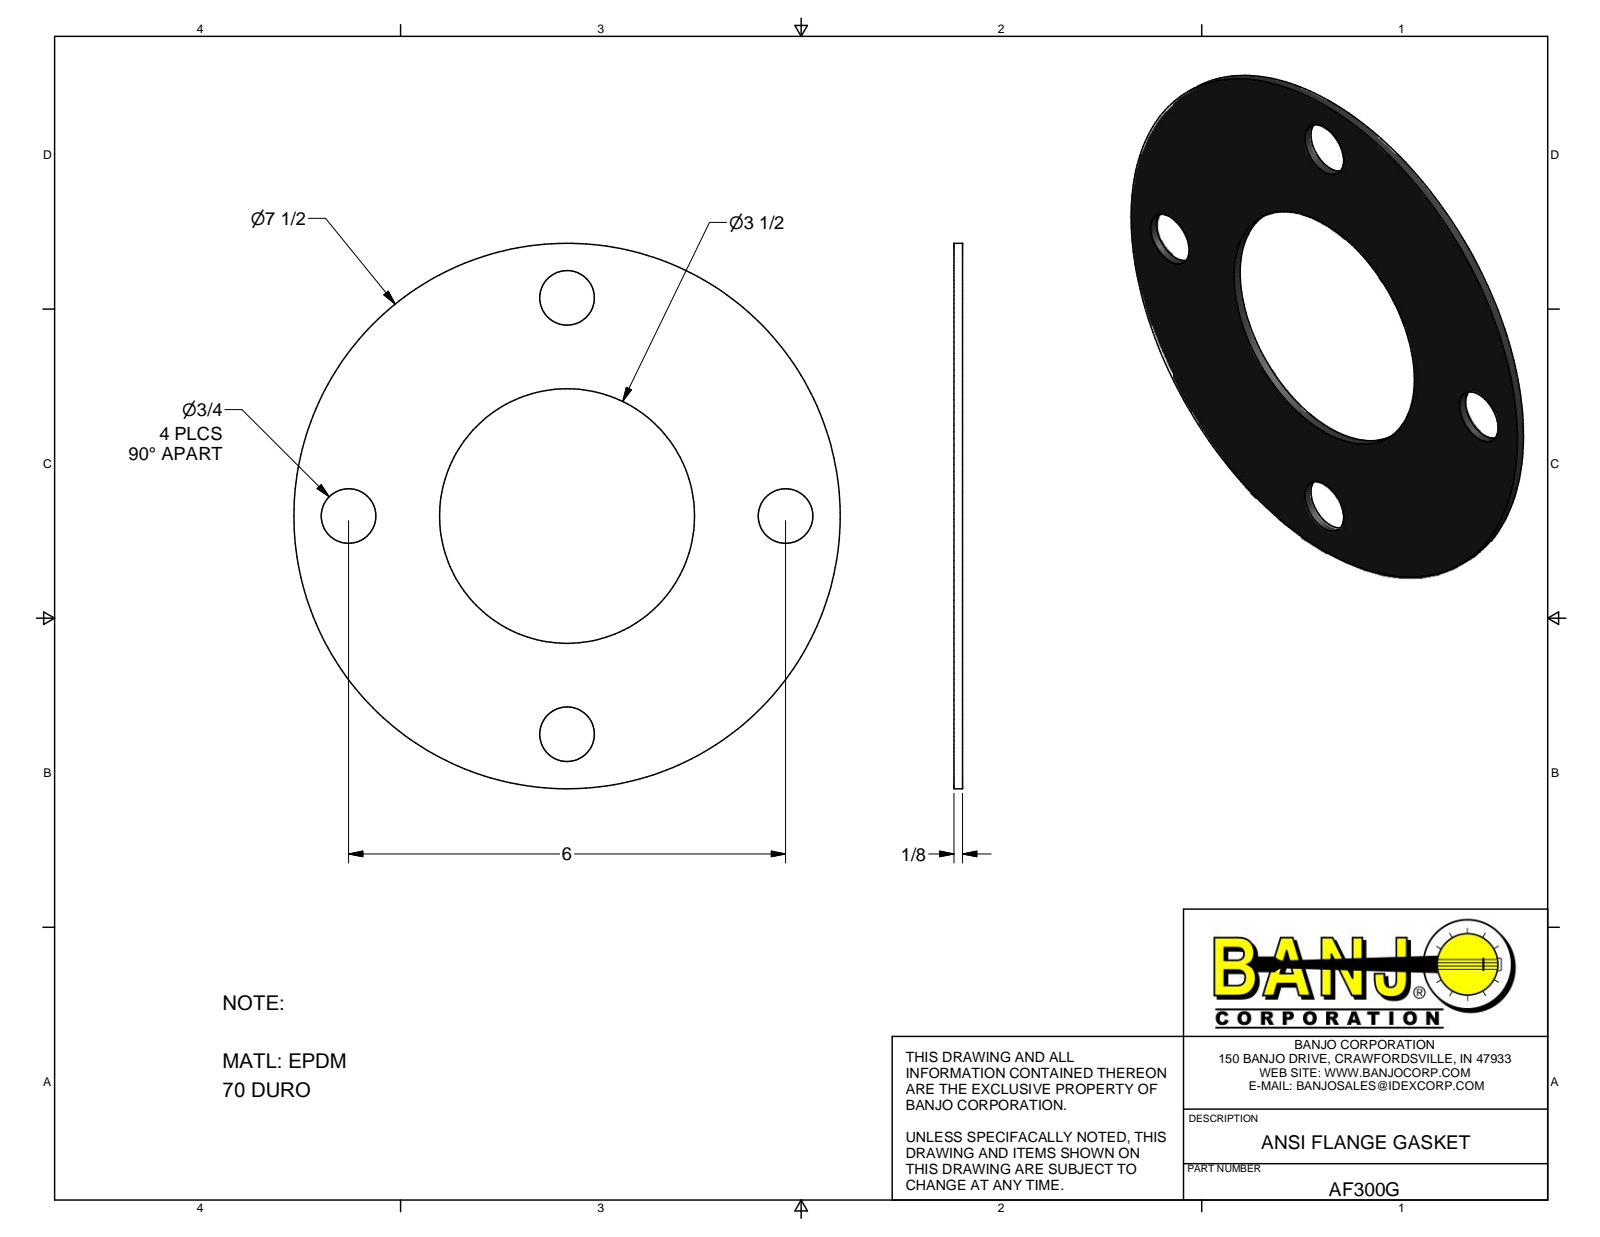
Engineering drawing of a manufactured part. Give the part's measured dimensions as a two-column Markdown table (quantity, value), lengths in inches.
| quantity | value |
| --- | --- |
| part name | AF300G |
| STEP written by | Autodesk Inventor 2014 (AUTOMOTIVE_DESIGN) |
| units | inches |
| bodies | 1 solid, 8 faces (2 planar, 6 cylindrical, 0 other) |
| overall size | 7.5 × 7.5 × 0.118 |
| volume | 3.869 in³ |
| surface area | 70.77 in² |
| round holes (diameter × count) | 0.75 × 4, 3.5 × 1 |
| round bosses / shafts (diameter × count) | 7.5 × 1 |
| main face-to-face distances | 0.118 |
| hole center spacings | 3, 4.243, 6 |
